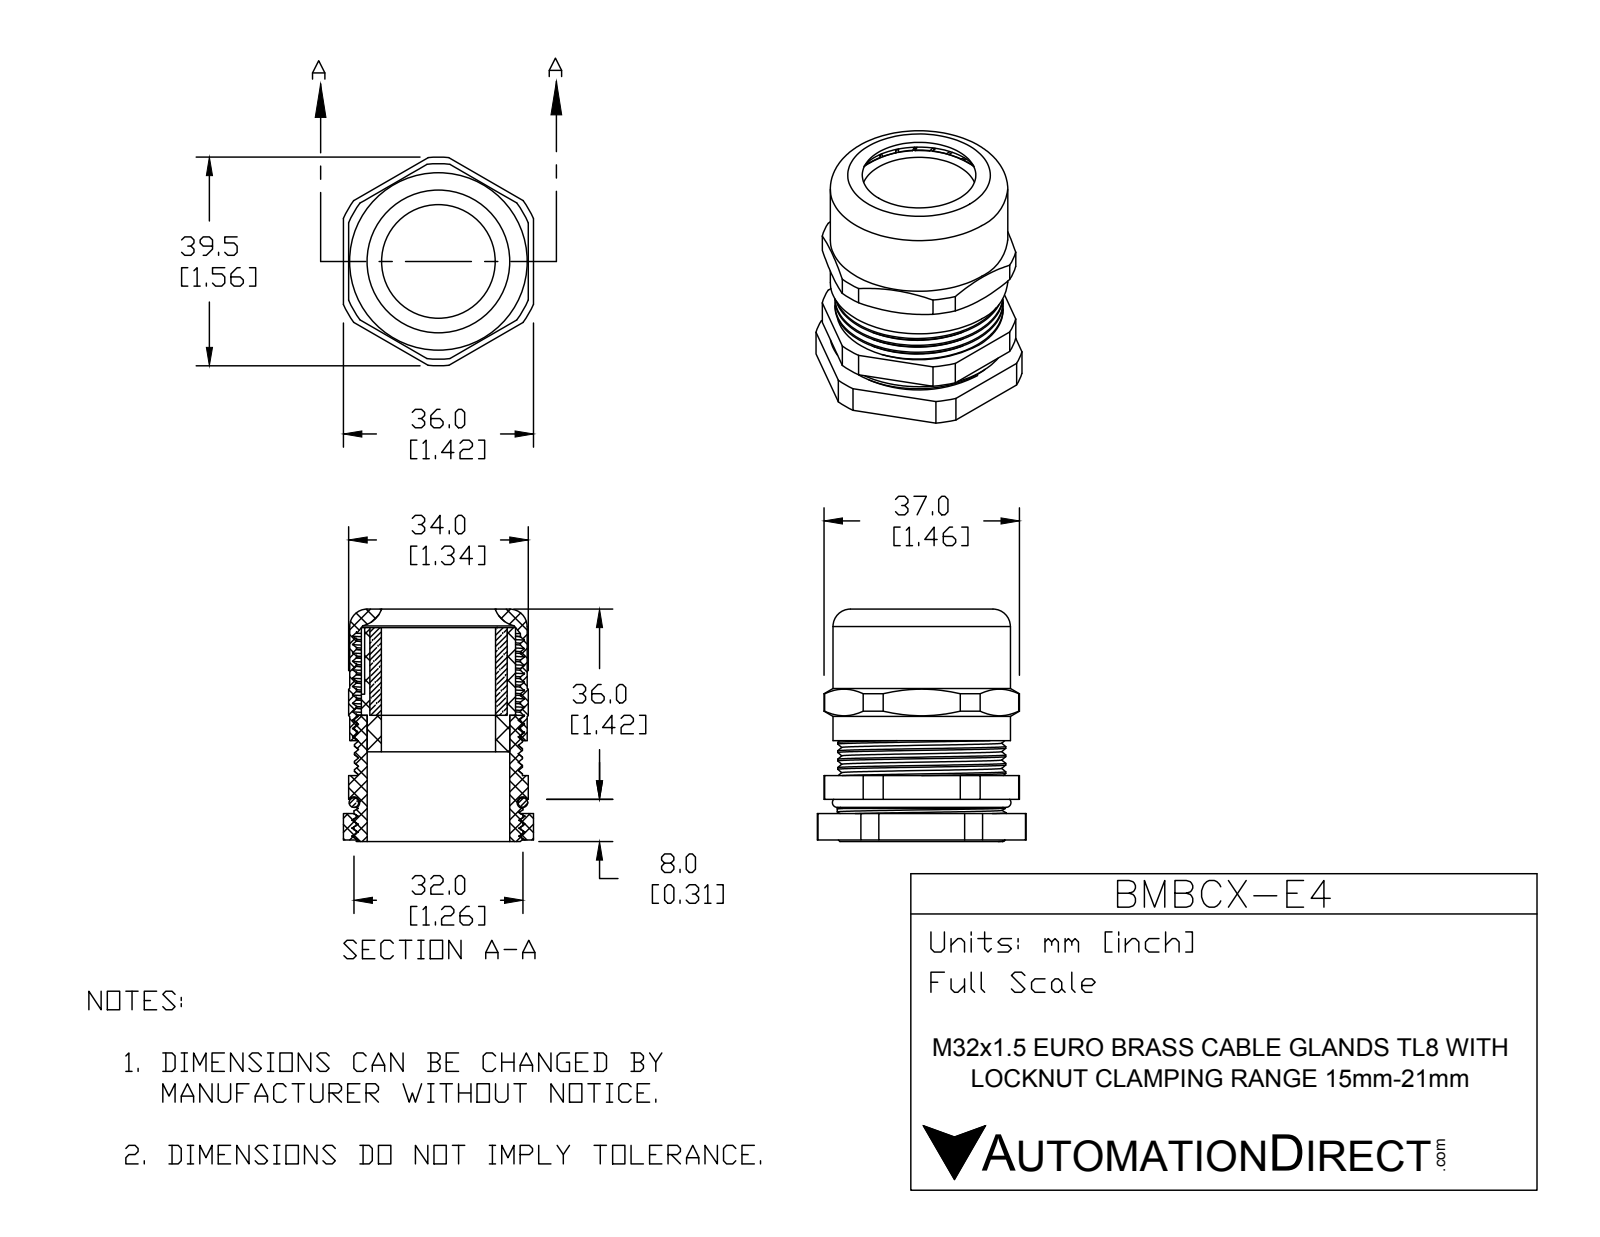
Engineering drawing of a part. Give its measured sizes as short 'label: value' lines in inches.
name: BMBCX-E4
written by: SolidWorks 2015 (CONFIG_CONTROL_DESIGN)
unit: in
bodies: 6 solids, 260 faces (132 planar, 97 cylindrical, 31 other)
size: 1.732 × 1.555 × 1.417
volume: 1.068 in³; area: 36.73 in²
holes: 1× ⌀0.85, 1× ⌀1.024, 1× ⌀1.063, 1× ⌀1.222, 1× ⌀1.228
bosses: 1× ⌀1.323, 1× ⌀1.26, 1× ⌀1.252, 1× ⌀1.15
rounds: 1× R0.728, 1× R0.778
face distances: 0.02, 0.039, 1.378, 1.339, 1.417, 0.732, 0.197, 0.929, 0.177, 1.583
